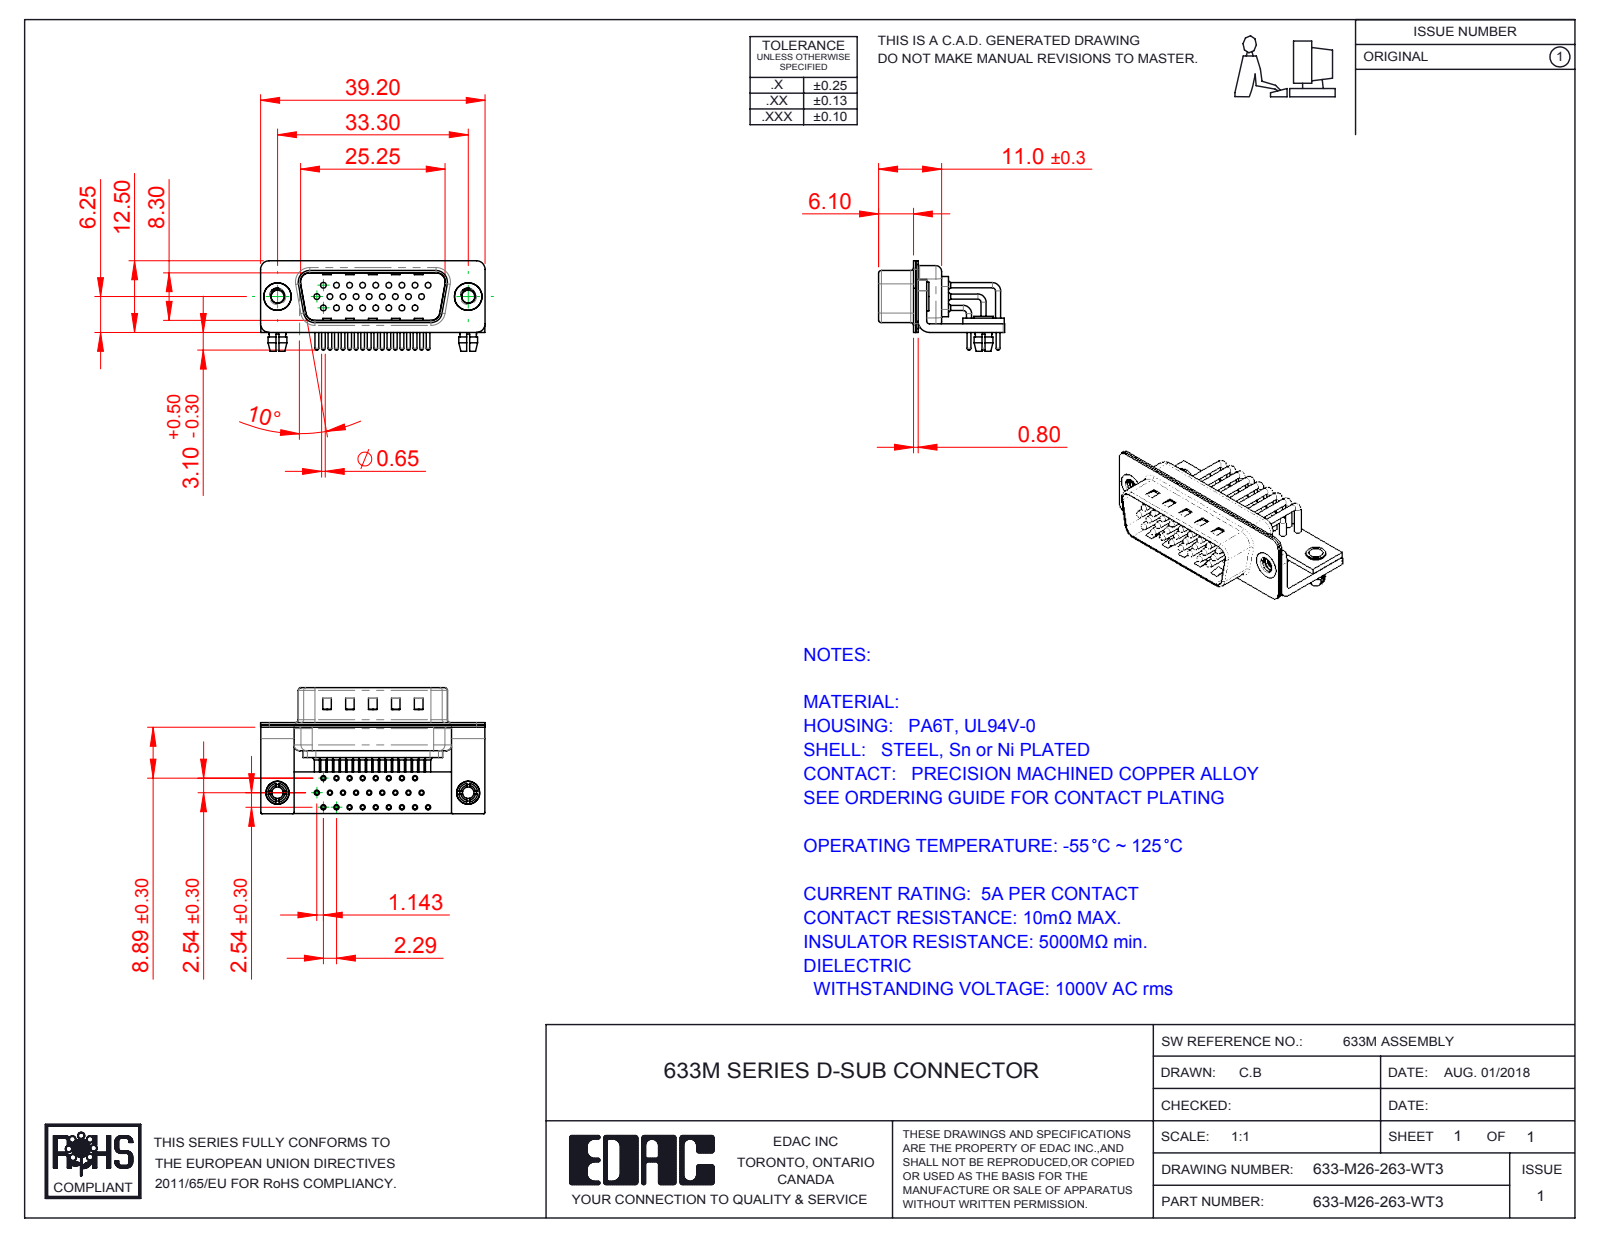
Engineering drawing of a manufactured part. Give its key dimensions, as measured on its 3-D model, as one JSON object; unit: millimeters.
{"part_name": "633M Board Lock; 633-M26-263-WT3; 633M 4-40 Threaded Rivet_Stabilizer; 633M Contact Row 3 (+7 more)", "step_written_by": "SolidWorks 2016 (CONFIG_CONTROL_DESIGN)", "units": "millimeters", "bodies": {"solids": 36, "faces": 3394, "planar": 1877, "cylindrical": 1175, "other": 342}, "overall_size": [39.2, 22, 15.8], "volume_mm3": 2666, "surface_area_mm2": 8233, "round_holes": [[2, 28], [0.9, 26], [1, 26], [1.7, 26], [2.26, 2], [2.5, 2], [3.2, 2], [4, 2], [4.8, 2]], "round_bosses_or_shafts": [[1.5, 26], [0.9, 26], [0.65, 26], [5, 2], [4.9, 2], [4, 2], [3.4, 2], [3.3, 2]], "partial_cylinders_radius": [[1.01, 26], [0.25, 16], [1.5, 16], [2, 13], [0.5, 9], [1.6, 8], [0.6, 4], [0.65, 4]], "face_to_face_distances": [0.4, 1.5, 0.85, 0.8, 1, 1.25, 1.9, 10.4, 9.55, 2.5], "hole_center_spacings": [4.57, 2.29, 2.28, 3.96, 6.86, 4.27, 6.05, 2.78]}
